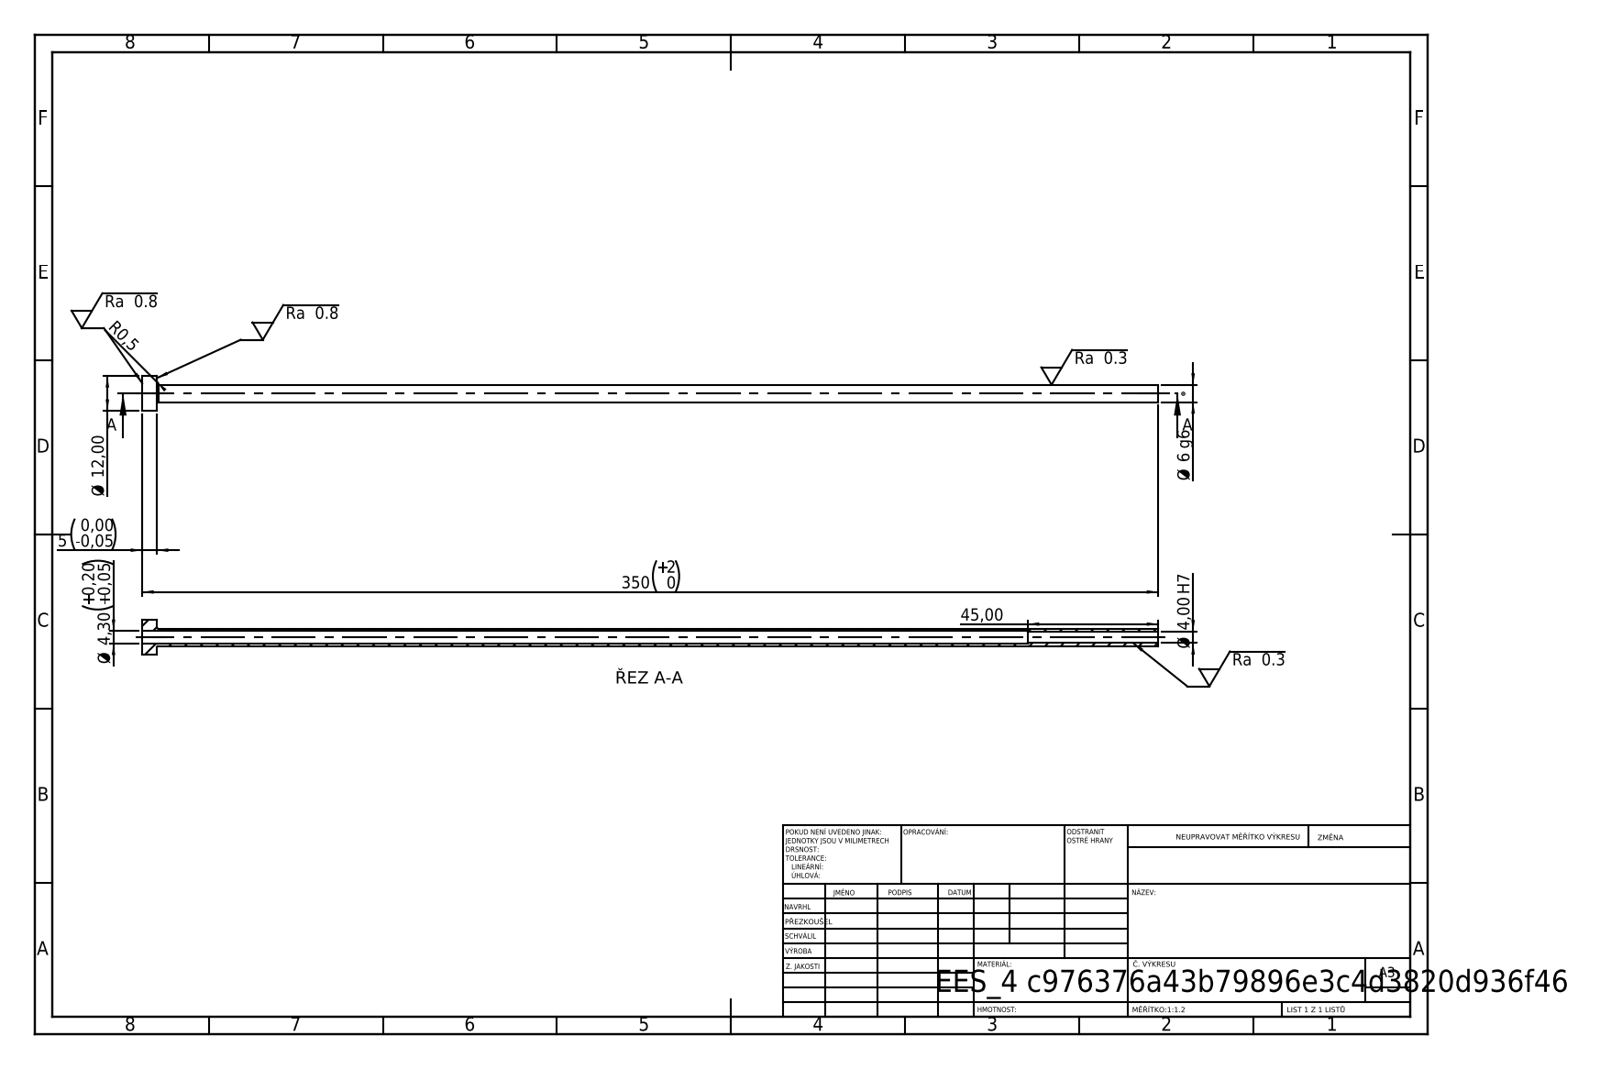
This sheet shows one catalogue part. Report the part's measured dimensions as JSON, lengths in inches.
{"step_written_by": "SolidWorks 2019 (CONFIG_CONTROL_DESIGN)", "units": "inches", "bodies": {"solids": 1, "faces": 14, "planar": 4, "cylindrical": 8, "other": 2}, "overall_size": [13.78, 0.472, 0.472], "volume_in3": 0.325, "surface_area_in2": 17.94, "round_holes": [[0.157, 1], [0.169, 1]], "round_bosses_or_shafts": [[0.472, 1], [0.236, 1]], "face_to_face_distances": [0.197, 13.78, 13.583, 12.008, 11.811, 1.772]}
